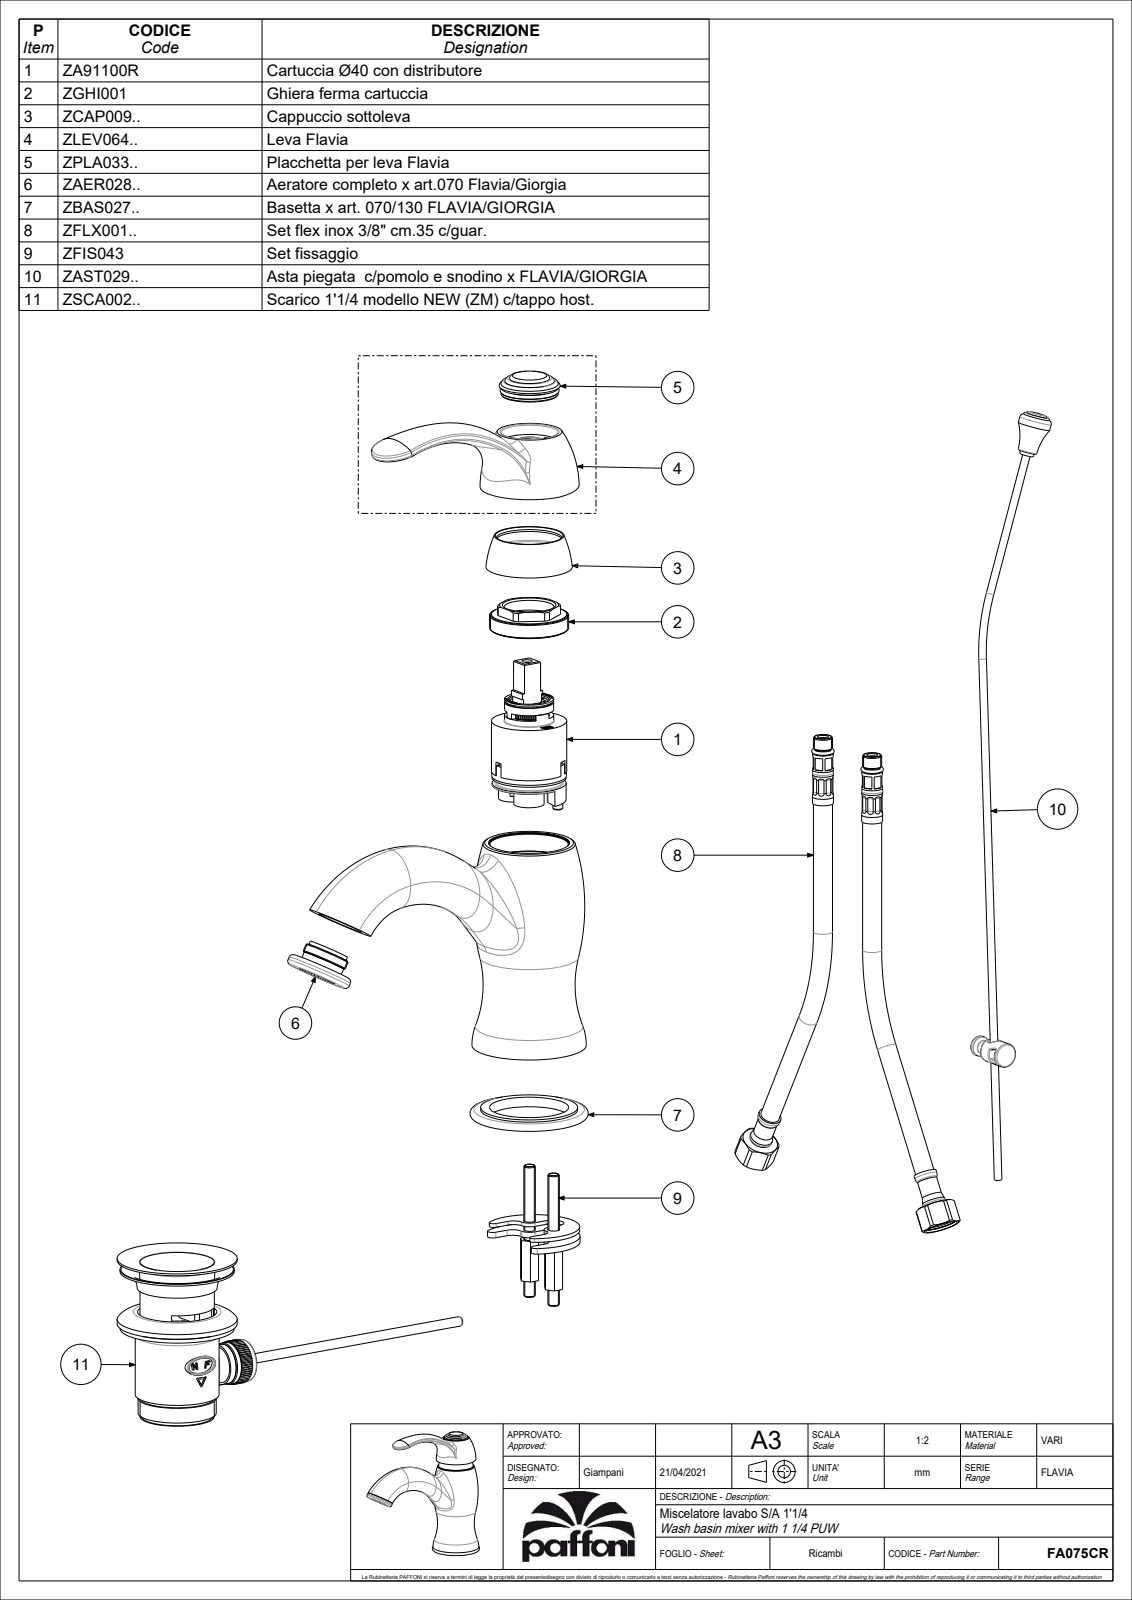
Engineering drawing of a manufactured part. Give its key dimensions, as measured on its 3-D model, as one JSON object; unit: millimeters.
{"part_name": "FA075CR", "step_written_by": "CREO PARAMETRIC BY PTC INC, 2020044 (CONFIG_CONTROL_DESIGN)", "units": "millimeters", "bodies": {"solids": 4, "faces": 2861, "planar": 2104, "cylindrical": 383, "other": 374}, "overall_size": [185.29, 164.93, 62], "volume_mm3": 223178, "surface_area_mm2": 129427, "round_holes": [[8, 4], [7, 3], [11, 3], [4, 2], [4.6, 2], [5, 2], [9, 2], [12, 2], [3.3, 1], [5.5, 1], [15, 1], [16, 1]], "round_bosses_or_shafts": [[15.9, 2], [10.8, 2], [9.4, 2], [8.5, 2], [8.2, 2], [6, 2], [4, 2], [50.9, 1]], "partial_cylinders_radius": [[0.5, 55], [0.2, 24], [1.5, 8], [0.3, 4], [2.5, 2], [5.5, 2], [6, 2], [7.5, 2]], "face_to_face_distances": [2.5, 75.9, 5, 5.5, 63.3, 10.6, 4, 3.5, 80.9, 7], "hole_center_spacings": [0.5, 2, 2.06, 7.92, 8.36, 8.6, 8.79, 9.01]}
